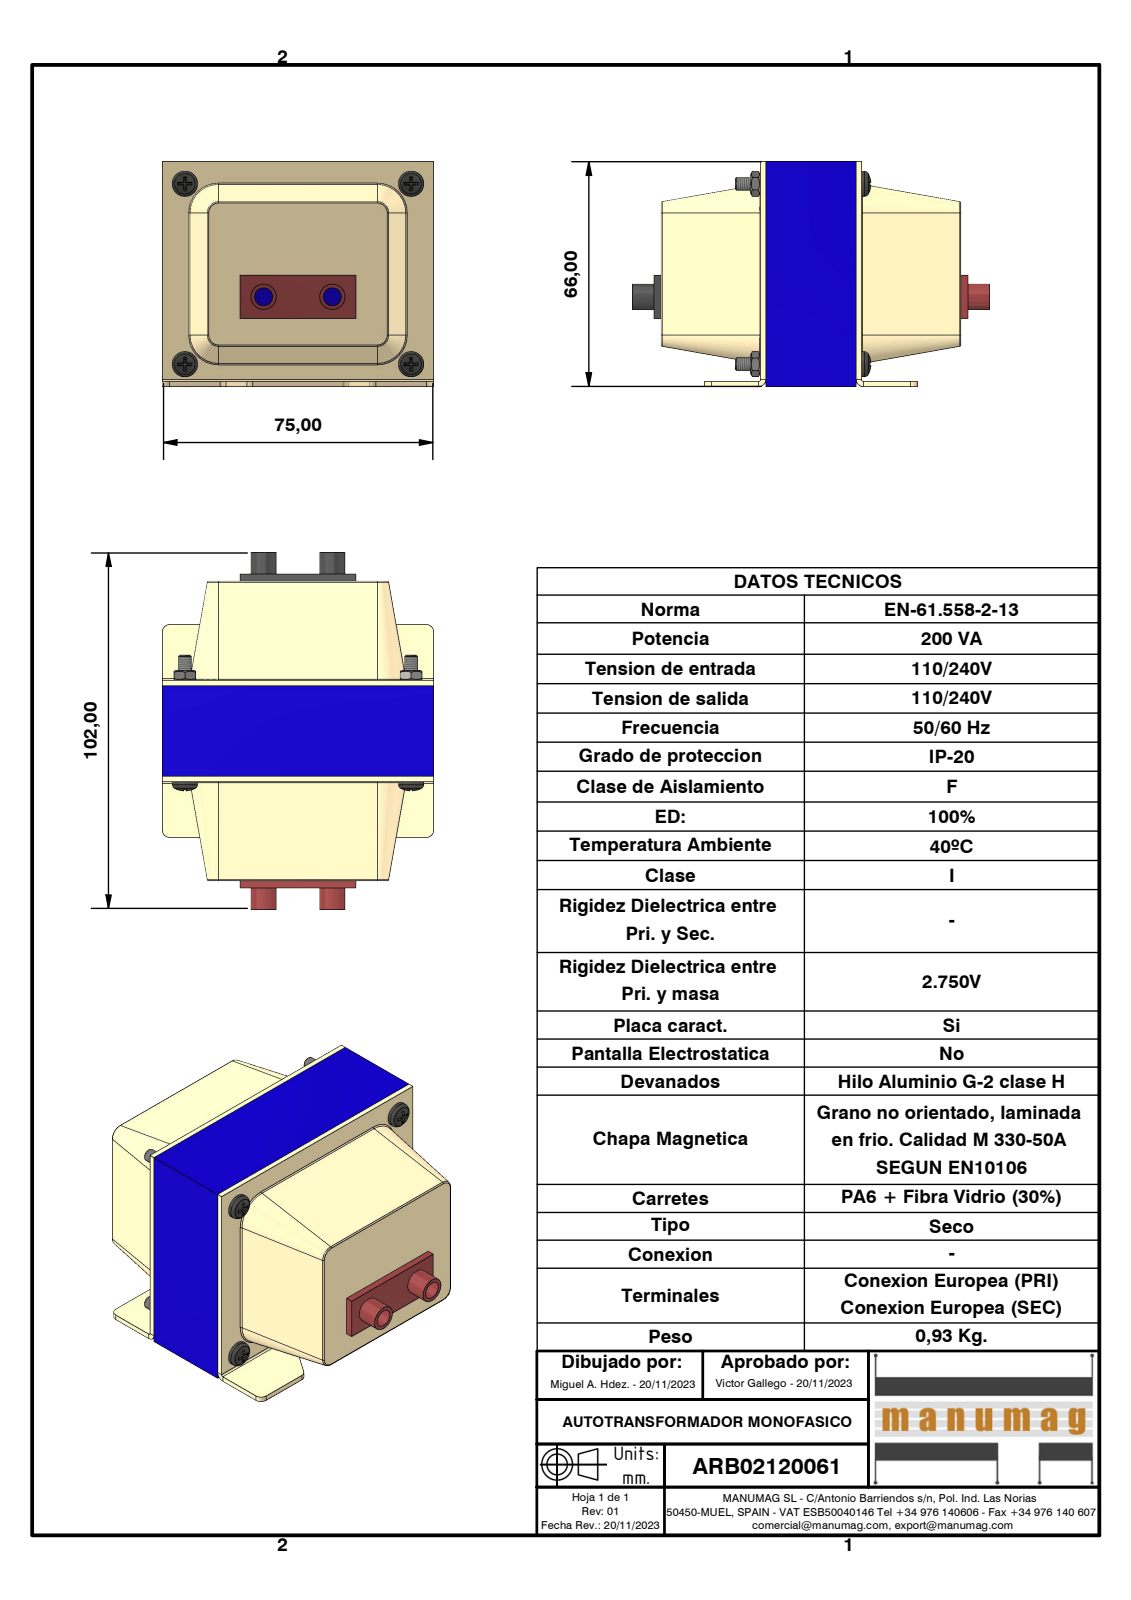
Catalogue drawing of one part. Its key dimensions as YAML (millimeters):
part_name: "ARB02120061; EI75 x 62,5 - 25 (RC25) Azul; TAPA RC25 RECEPTACULO; Receptaculo negro (+3 more)"
step_written_by: "Autodesk Inventor 2023 (AUTOMOTIVE_DESIGN)"
units: millimeters
bodies: {solids: 13, faces: 350, planar: 162, cylindrical: 64, other: 124}
overall_size: [99, 75, 62.5]
volume: 111042
surface_area: 64915
round_holes:
  - {diameter: 2.85, count: 4}
  - {diameter: 3, count: 4}
  - {diameter: 4.5, count: 4}
  - {diameter: 5, count: 2}
round_bosses_or_shafts:
  - {diameter: 3.5, count: 4}
  - {diameter: 3.18, count: 4}
  - {diameter: 7, count: 2}
partial_cylinders:
  - {radius: 0.38, count: 16}
  - {radius: 2, count: 14}
  - {radius: 0.5, count: 2}
face_to_face_distances: [25, 1.5, 54, 27.5, 12.5, 53.58, 50, 62.5, 29, 63.43]
hole_center_spacings: [28.67, 38.13, 44.83, 50, 51.4, 62.5, 80.04, 19]
